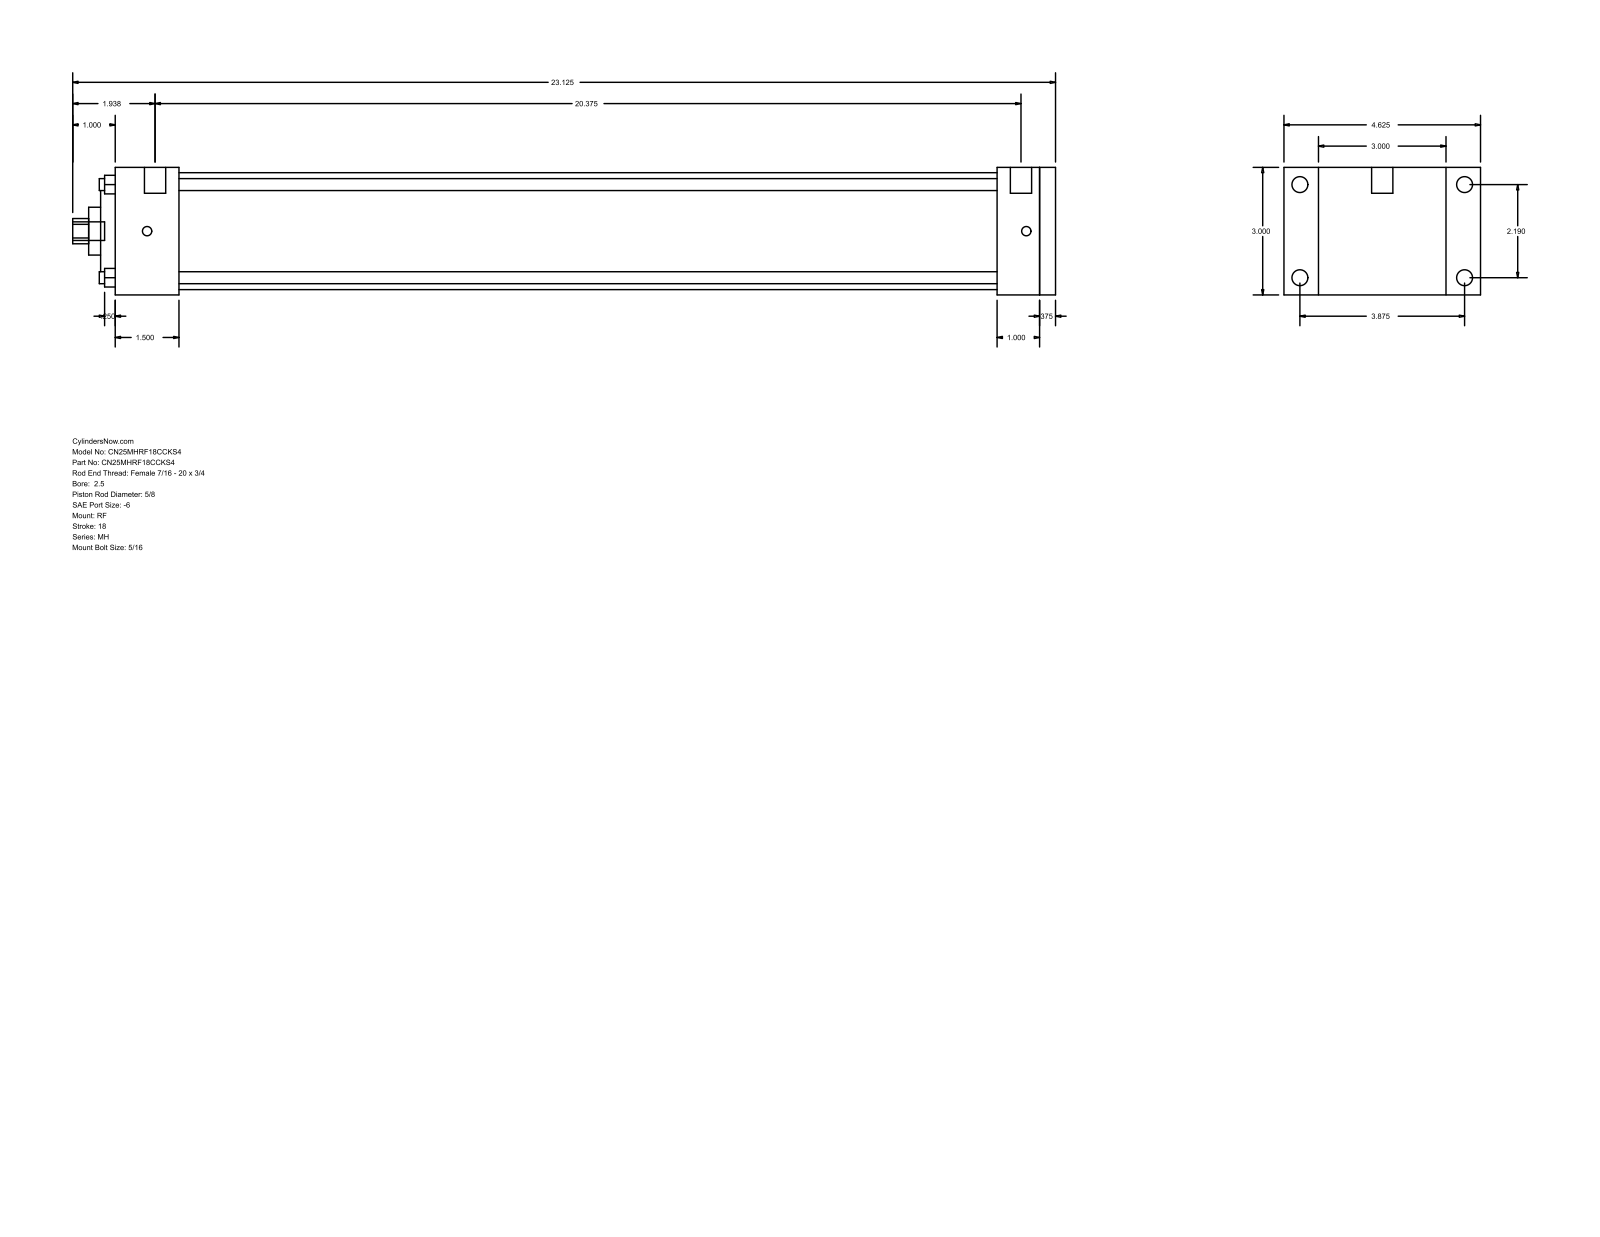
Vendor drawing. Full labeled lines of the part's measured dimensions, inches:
Part name (STEP PRODUCT): MH_RF__0250_0.625
STEP written by: GSSL Pune (CONFIG_CONTROL_DESIGN)
Units: inches
Bodies: 0 solids, 94 faces (65 planar, 29 cylindrical, 0 other)
Overall size (bounding box): 23.125 × 4.625 × 3
Round holes (diameter × count): ⌀0.281 ×4, ⌀0.625 ×1, ⌀1.125 ×1, ⌀2.187 ×1, ⌀2.75 ×1
Round bosses / shafts (diameter × count): ⌀0.375 ×4, ⌀0.219 ×4, ⌀0.5 ×2, ⌀0.437 ×1
Partial cylindrical surfaces — rounded edges, fillets, slot ends (radius × count): R0.297 ×1
Main face-to-face distances: 3, 0.375, 22.125, 21.75, 1, 20.75, 1.375, 1.5, 19.25, 20.25
Hole centre spacings: 1.548, 2.19, 3.097
